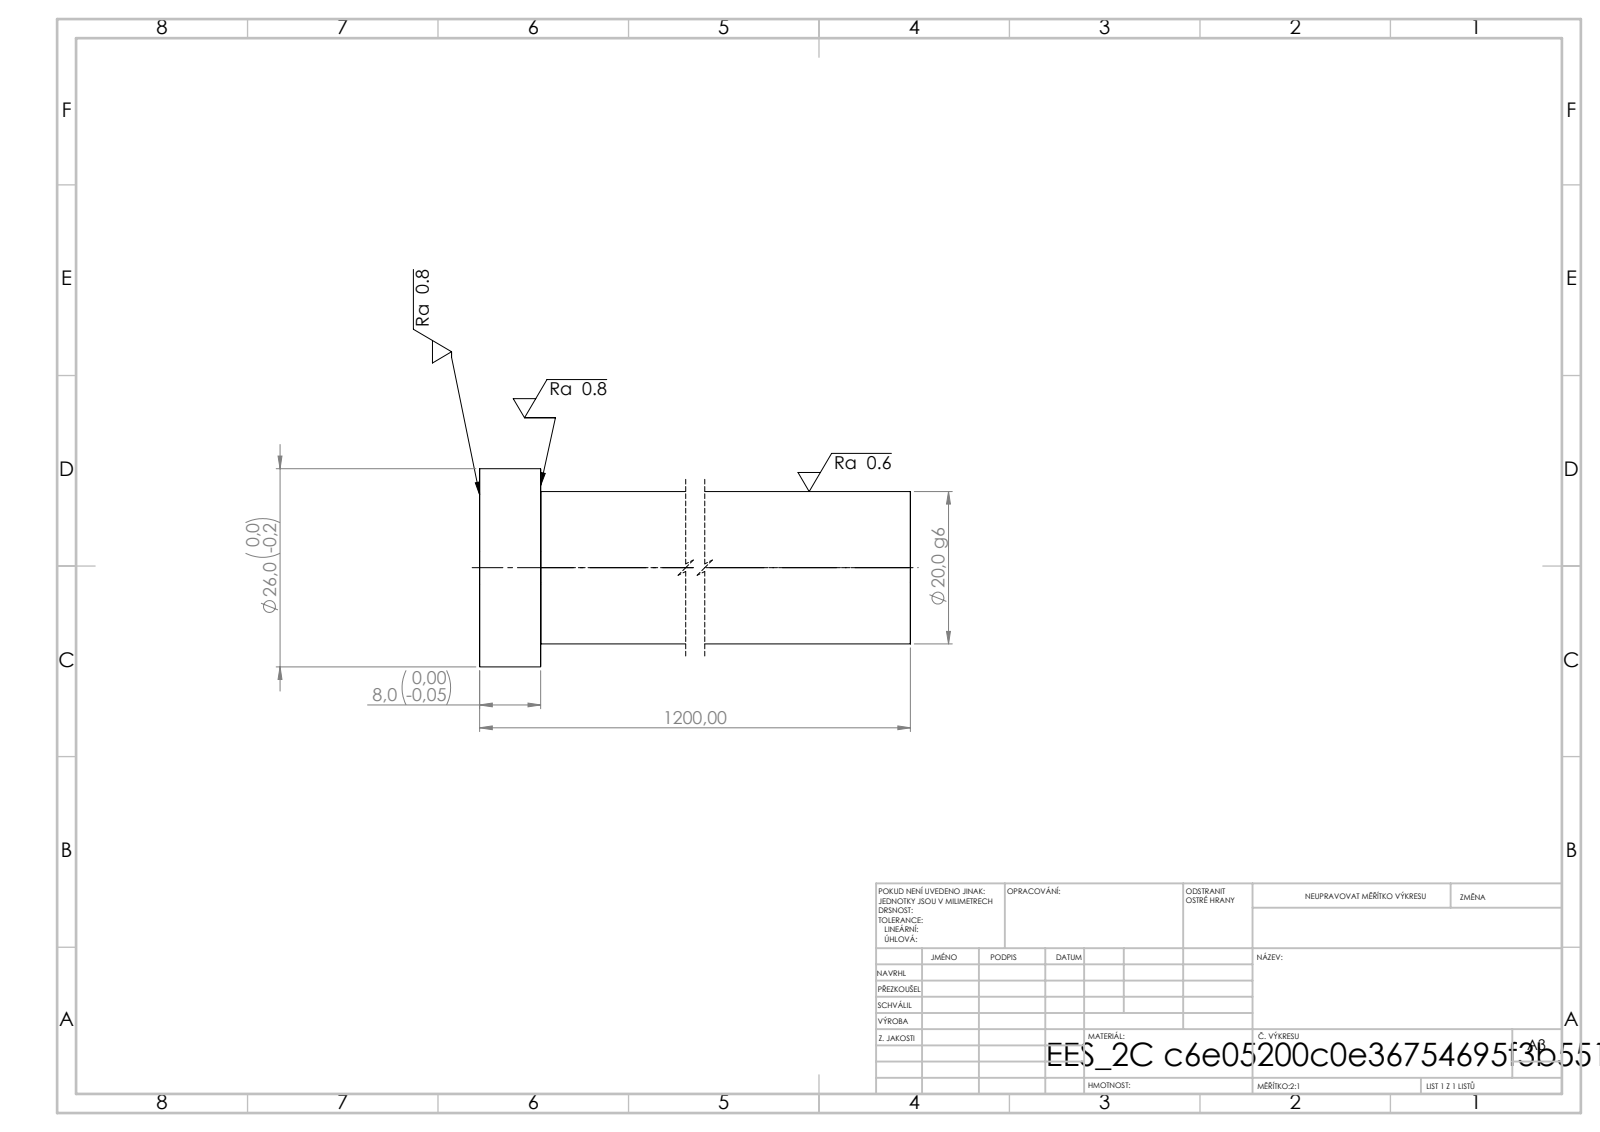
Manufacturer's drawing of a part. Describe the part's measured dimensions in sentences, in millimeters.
Its 3-D file was written by "SolidWorks 2019 (CONFIG_CONTROL_DESIGN)". It is 1 solid with 7 faces: 3 planar, 4 cylindrical and 0 other. Overall it measures 1200 by 26 by 26 millimeters. Its volume is 378 725 cubic millimeters and its surface area 76 611 square millimeters. Round bosses or shafts: 1 of diameter 26, 1 of diameter 20. The main face-to-face distances are 1200, 8, 1192.
